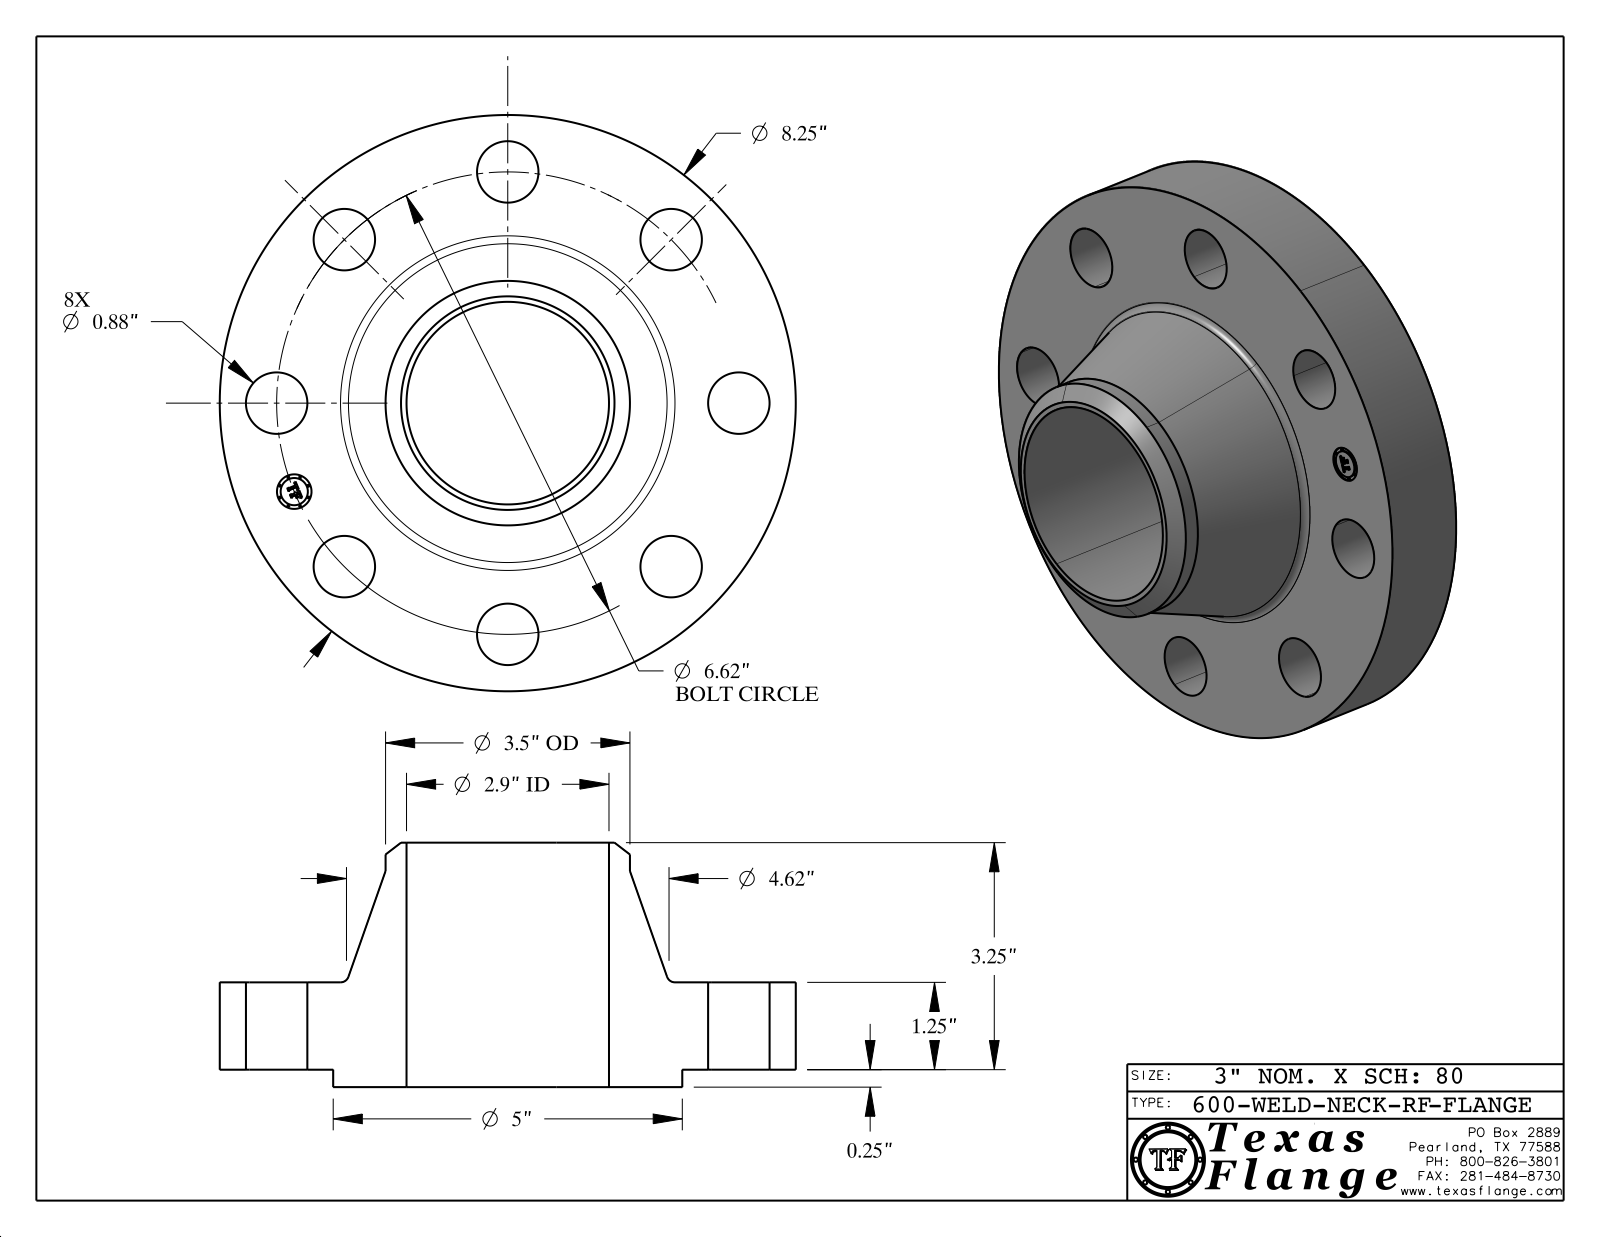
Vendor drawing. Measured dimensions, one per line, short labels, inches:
name: 600-WELD-NECK-RF
written by: CATIA V5 STEP AP214 (AUTOMOTIVE_DESIGN)
unit: in
bodies: 1 solid, 419 faces (369 planar, 44 cylindrical, 6 other)
size: 8.25 × 8.25 × 3.5
volume: 67.02 in³; area: 197.2 in²
holes: 8× ⌀0.88, 1× ⌀0.495, 1× ⌀2.9
bosses: 8× ⌀0.03, 1× ⌀8.25, 1× ⌀5, 1× ⌀3.5, 1× ⌀0.39
face distances: 1.25, 0.25, 1.5, 3.5, 3.25, 2, 0.015, 1.485, 1.235, 2.015
hole spacings: 3.31, 2.533, 6.116, 4.681, 4.681, 1.291, 3.678, 6.493
